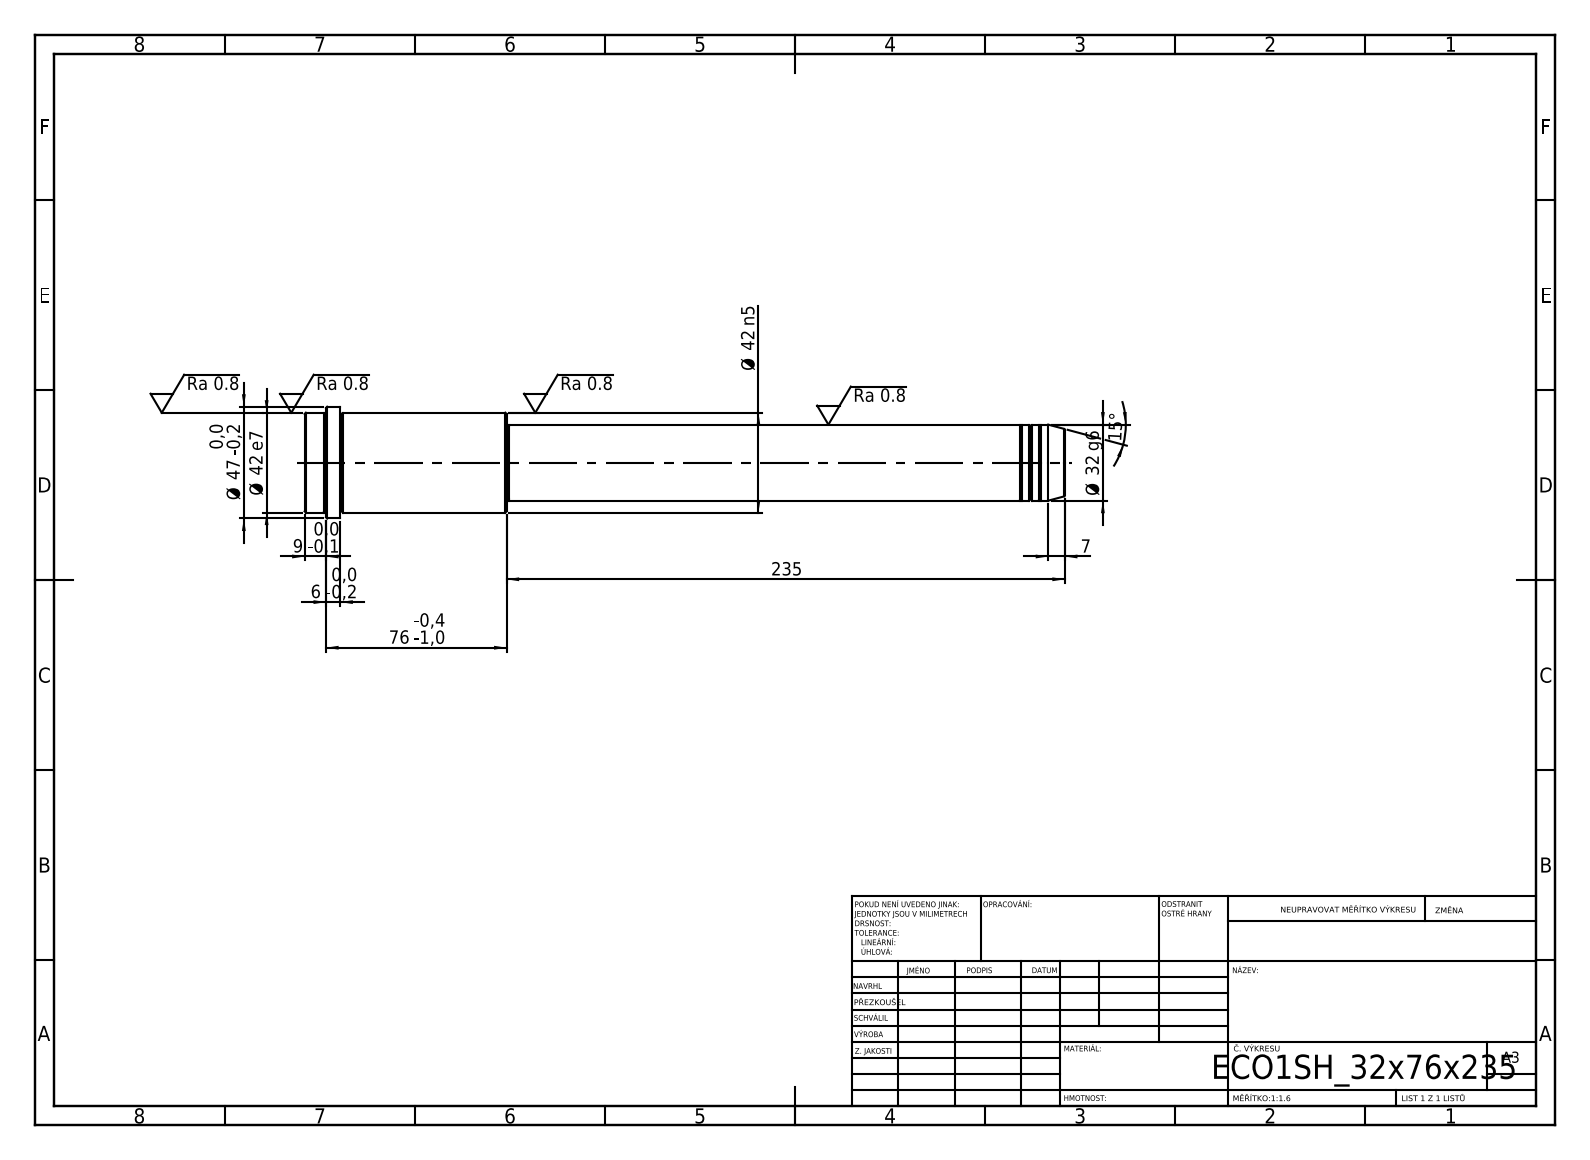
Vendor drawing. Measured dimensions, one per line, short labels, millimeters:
written by: SolidWorks 2019 (CONFIG_CONTROL_DESIGN)
unit: mm
bodies: 1 solid, 52 faces (6 planar, 16 cylindrical, 30 other)
size: 320 × 47 × 47
volume: 307 901 mm³; area: 38 480 mm²
bosses: 1× ⌀47, 1× ⌀42, 1× ⌀32, 1× ⌀31
face distances: 320, 235, 85, 305, 70, 15, 311, 76, 6, 9
